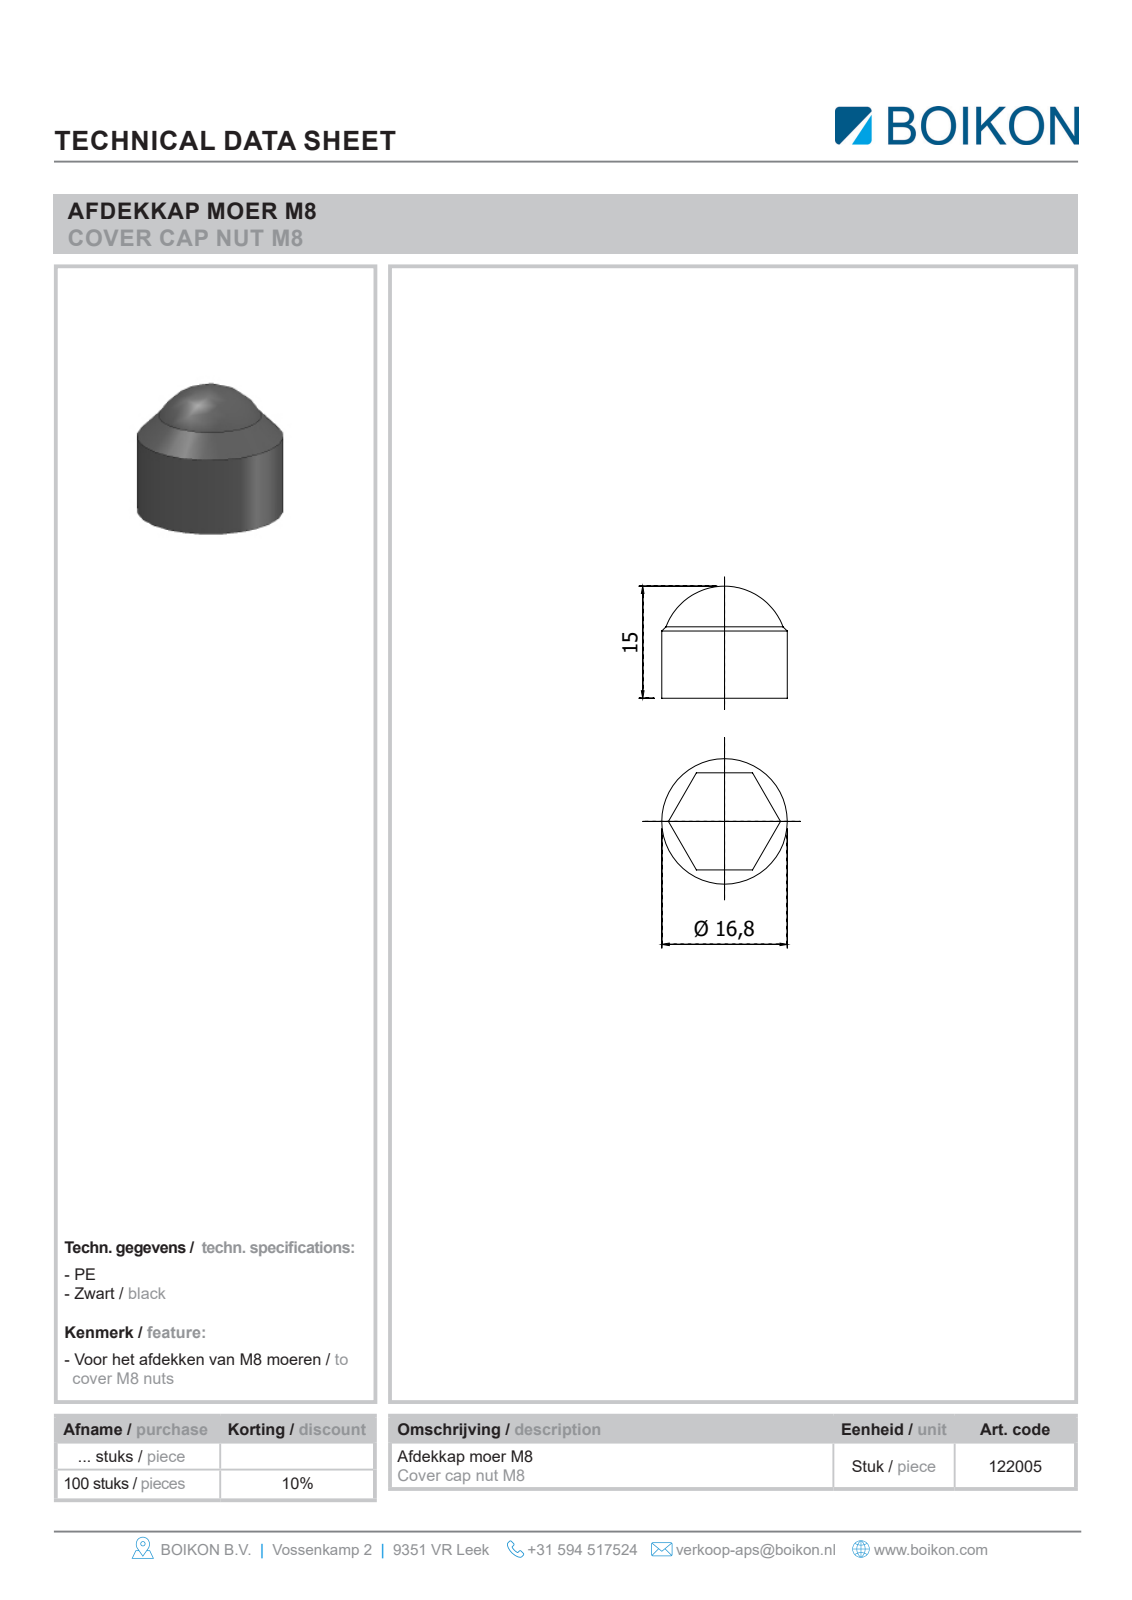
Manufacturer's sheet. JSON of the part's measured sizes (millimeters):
{"part_name": "Root; 122005Afdekkap voor moer M8BOIKON", "step_written_by": "HiCAD 2013 1802.4 Build 509 (AUTOMOTIVE_DESIGN)", "units": "millimeters", "bodies": {"solids": 1, "faces": 11, "planar": 8, "cylindrical": 1, "other": 2}, "overall_size": [17.5, 16.8, 16.8], "volume_mm3": 1956, "surface_area_mm2": 1206, "round_bosses_or_shafts": [[16.8, 1]], "face_to_face_distances": [13, 4.5]}
